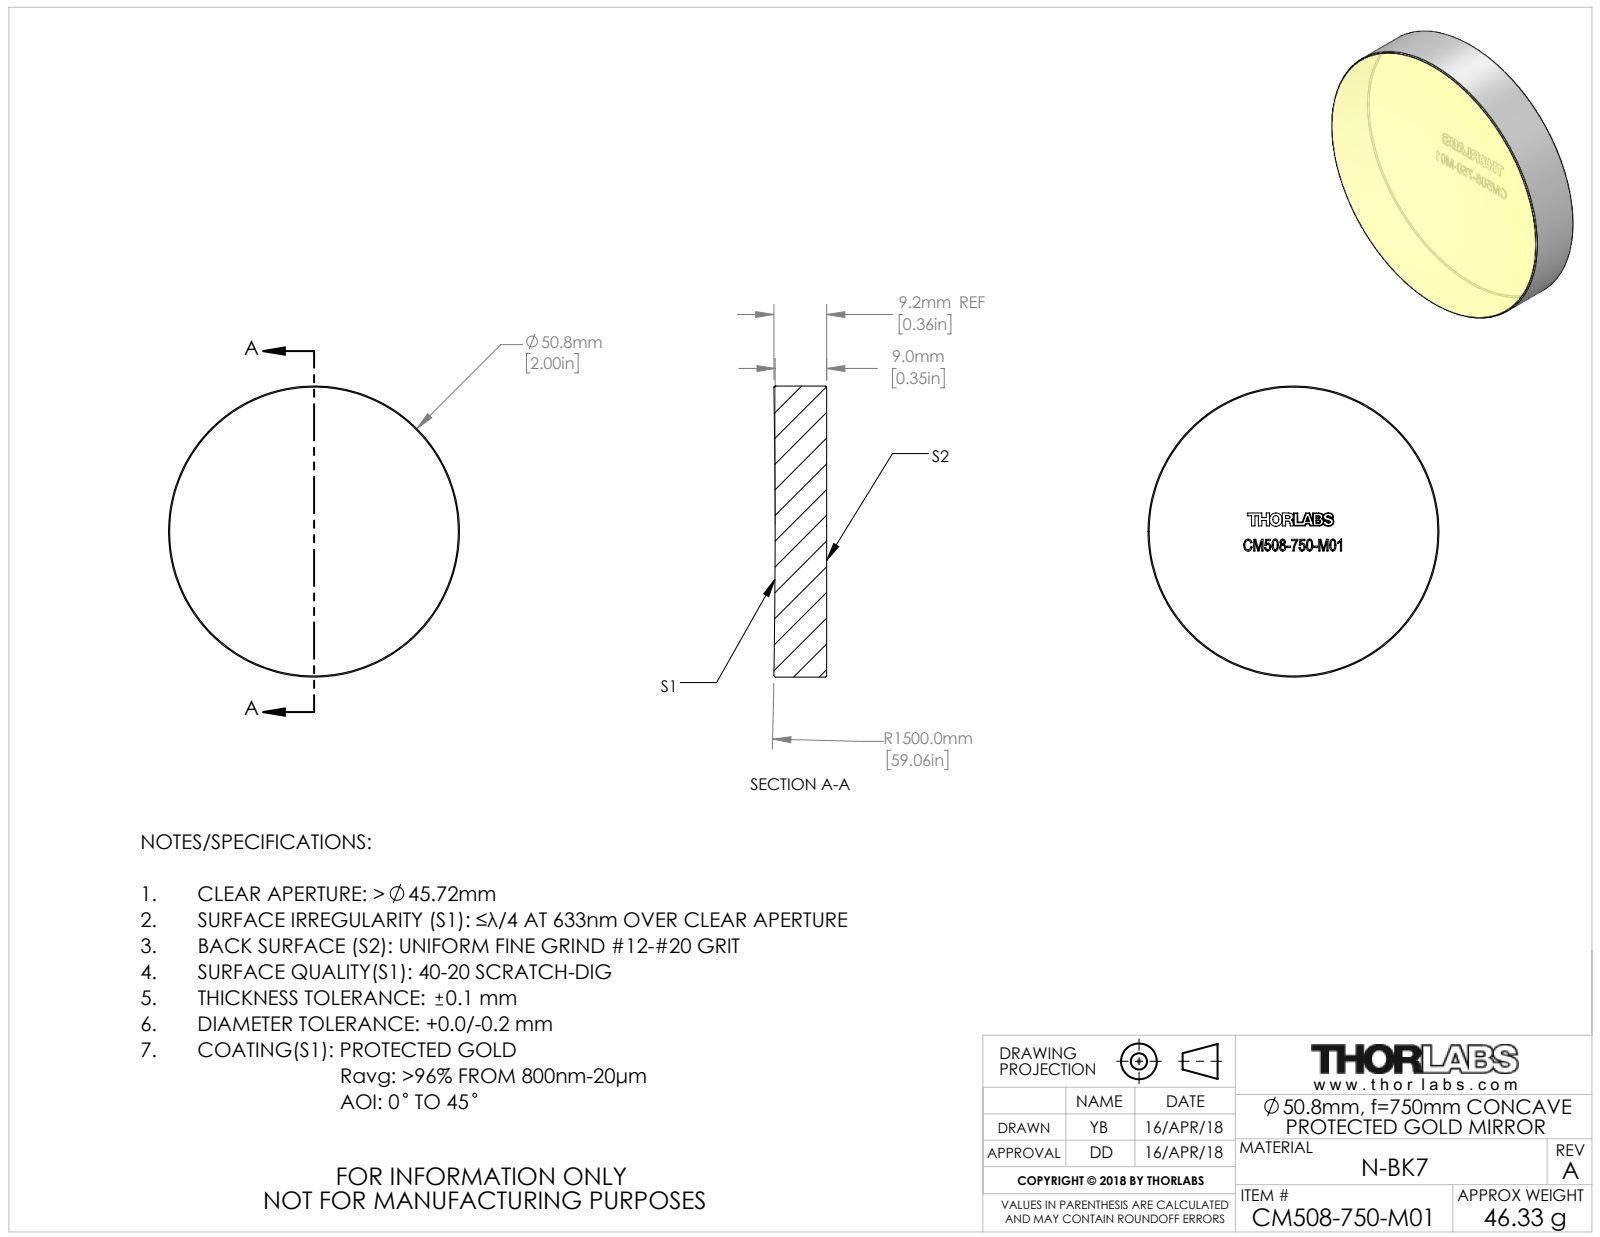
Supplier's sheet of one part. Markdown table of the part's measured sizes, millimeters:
| quantity | value |
| --- | --- |
| part name | TTN153331-E0W |
| STEP written by | SolidWorks 2018 (CONFIG_CONTROL_DESIGN) |
| units | millimeters |
| bodies | 1 solid, 42 faces (34 planar, 2 cylindrical, 6 other) |
| overall size | 50.8 × 50.8 × 9.21 |
| volume | 18 453 mm³ |
| surface area | 5 487 mm² |
| round bosses / shafts (diameter × count) | 50.8 × 1 |
